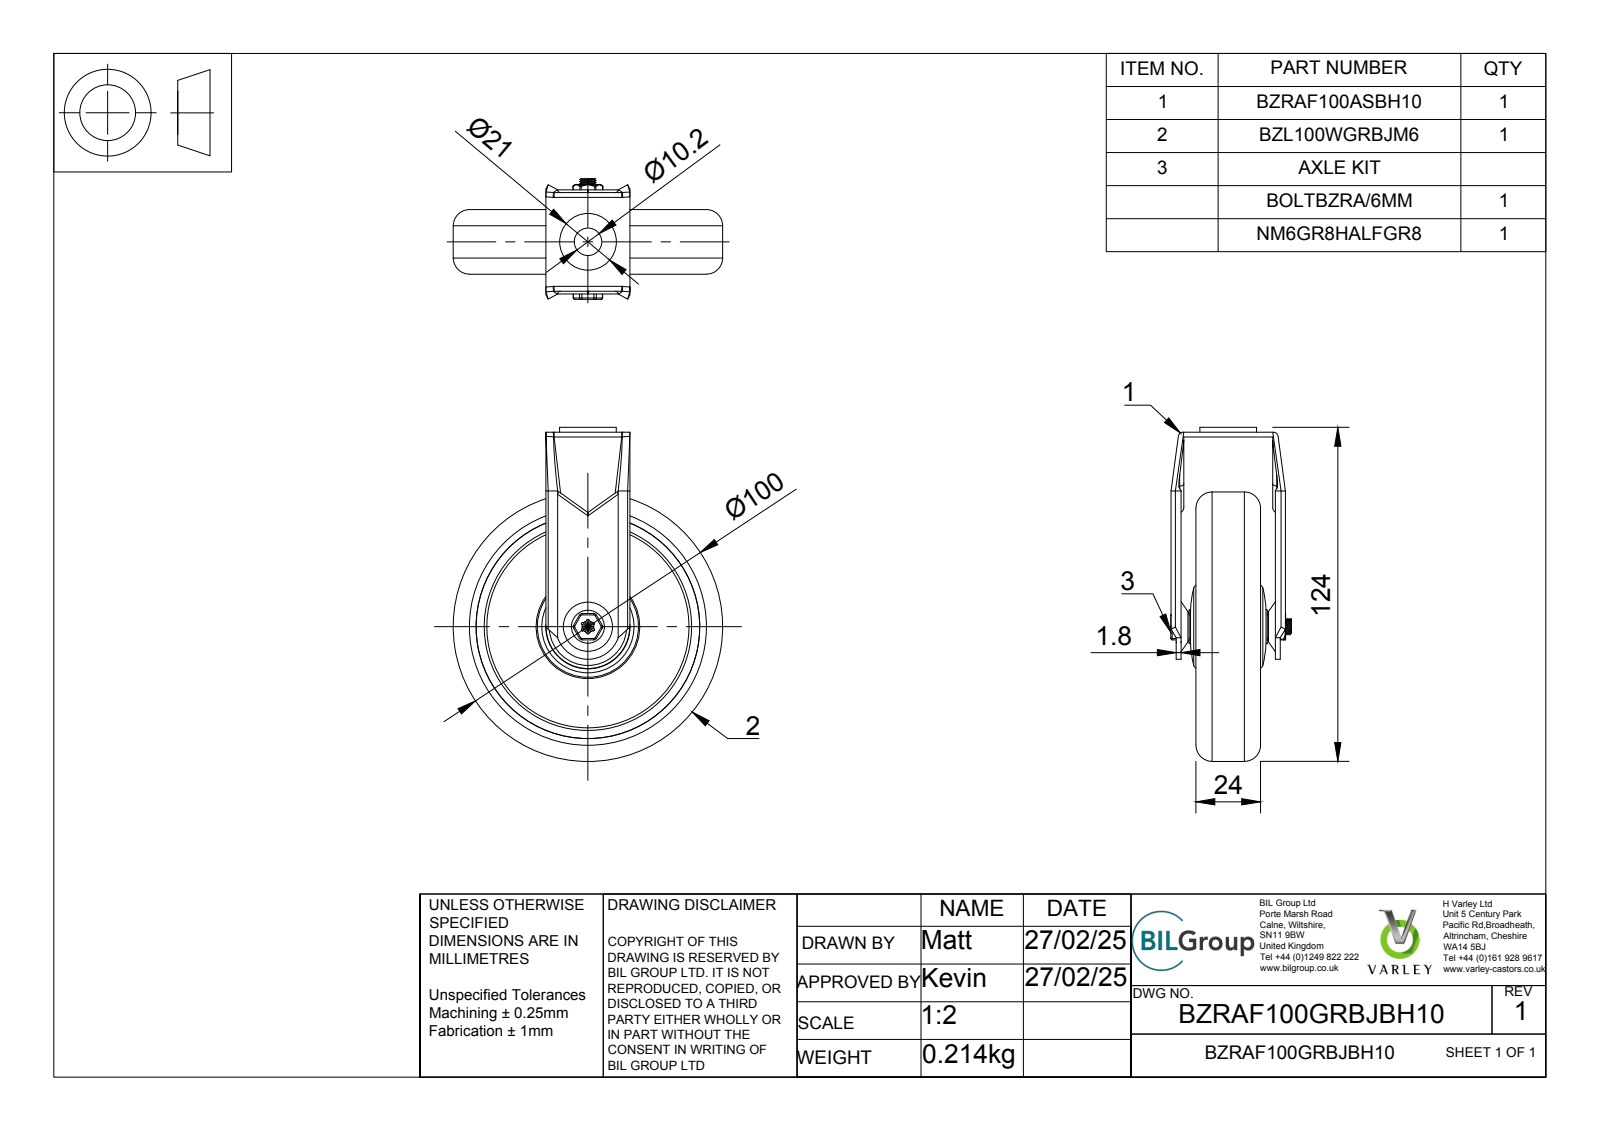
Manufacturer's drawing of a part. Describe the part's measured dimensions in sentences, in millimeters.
The part is named "BZRAF100GRBJBH10 v2; BZRAF100ASBH10 v1; ZINC PLATED PRESSED STEEL FORKS; BZL100WGRBJM6 v1 (+7 more)". Its 3-D file was written by "Autodesk Translation Framework v13.20.0.188 (AP242_MANAGED_MODEL_BASED_3D_ENGINEERING_MIM_LF)". It is 20 solids with 468 faces: 139 planar, 182 cylindrical and 147 other. Overall it measures 124 by 100 by 45 millimeters. Its volume is 117 328 cubic millimeters and its surface area 67 854 square millimeters. Round holes: 1 of diameter 6, 1 of diameter 6.1, 1 of diameter 6.2, 1 of diameter 7, 1 of diameter 8.2, 1 of diameter 10, 1 of diameter 10.2, 1 of diameter 14.8, 1 of diameter 15.1, 1 of diameter 21.7, 1 of diameter 22.6, 1 of diameter 23.5. Round bosses or shafts: 1 of diameter 100, 1 of diameter 37.5, 1 of diameter 31, 1 of diameter 27.25, 1 of diameter 22.1, 1 of diameter 21, 1 of diameter 15.5, 1 of diameter 13.7. Partial cylindrical surfaces (rounded edges, fillets, slot ends): 26 of radius 1, 12 of radius 0.5, 8 of radius 1.5, 8 of radius 2.5, 6 of radius 0.4, 4 of radius 0.99, 2 of radius 1.8, 1 of radius 2.12. The main face-to-face distances are 1.8, 14, 4, 10, 5.5, 15.5, 1, 35.8, 19.5, 29.5.
